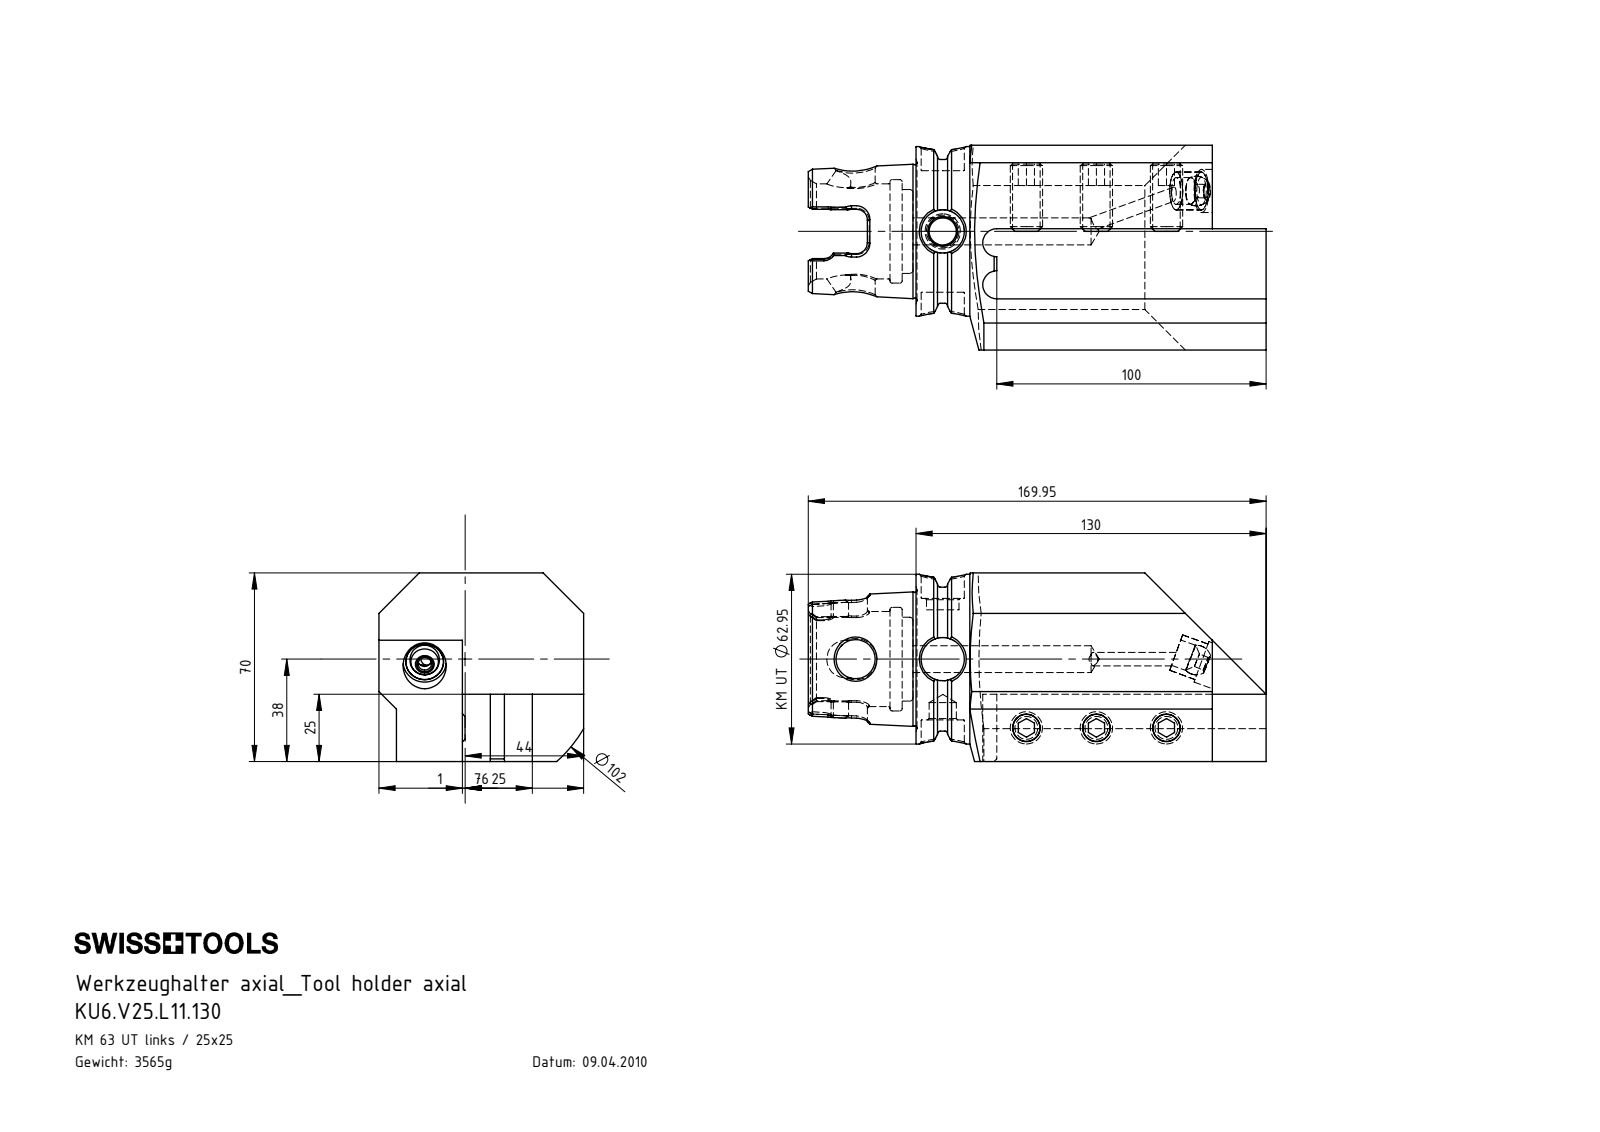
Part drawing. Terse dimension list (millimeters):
name: KU1-U14.001.012_2; KU6-V25.L11.130_A; KU6.V25.L11.130; KU1-U14.001.012 (+2 more)
written by: SolidWorks 2017 (CONFIG_CONTROL_DESIGN)
unit: mm
bodies: 6 solids, 317 faces (98 planar, 75 cylindrical, 144 other)
size: 169.95 × 76 × 70
volume: 454 708 mm³; area: 63 784 mm²
holes: 3× ⌀10.2, 2× ⌀5, 2× ⌀10, 2× ⌀16.05, 1× ⌀10.1, 1× ⌀12.1, 1× ⌀14, 1× ⌀14.5, 1× ⌀16, 1× ⌀31.1, 1× ⌀35.27, 1× ⌀38.4
bosses: 3× ⌀12, 1× ⌀62.95, 1× ⌀14
rounds: 6× R4, 2× R5.2, 2× R7.04, 1× R27.85, 1× R51
face distances: 45, 25, 70, 19, 76, 57, 26, 31, 69.5, 50.5
hole spacings: 26, 32.35, 40.18, 52, 62.49, 68.34, 86.88, 92.97
